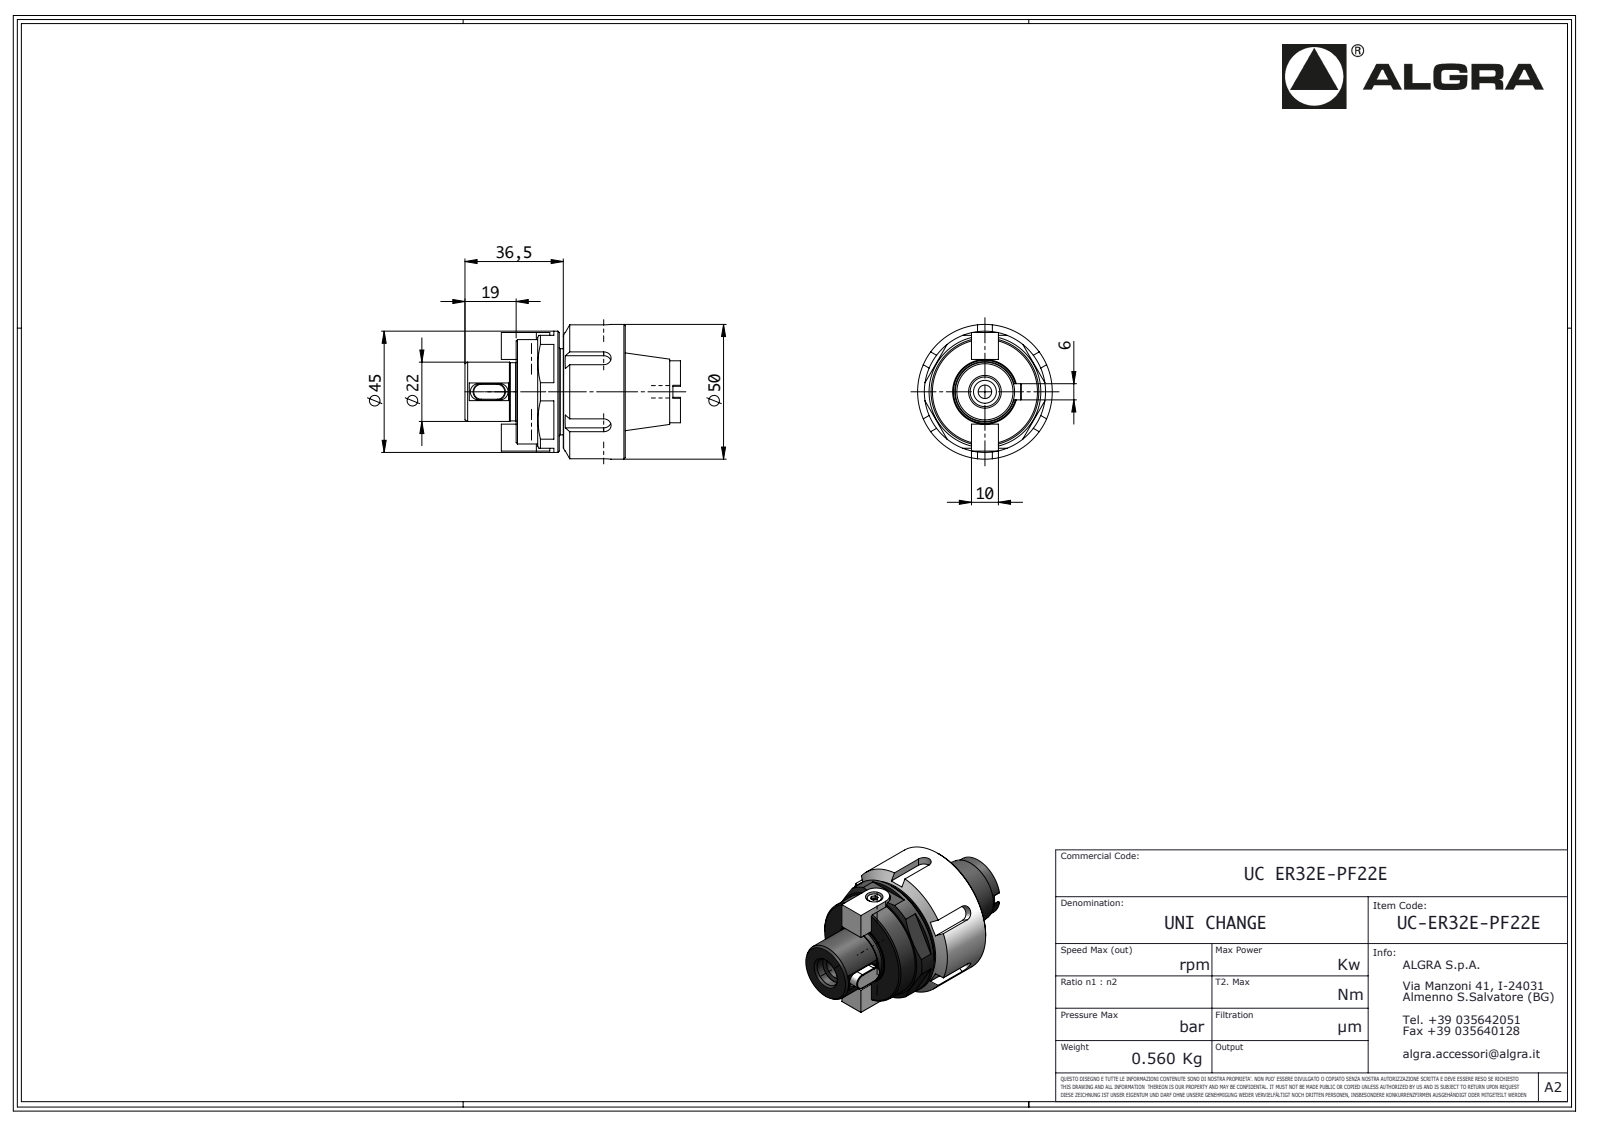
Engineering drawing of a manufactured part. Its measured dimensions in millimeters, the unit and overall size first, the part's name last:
Units: millimetres
Overall size (bounding box): 91.7 × 50 × 50
Round holes (diameter × count): ⌀2.1 ×1
Round bosses / shafts (diameter × count): ⌀50 ×1, ⌀45 ×1, ⌀40 ×1, ⌀31.6 ×1, ⌀23.65 ×1, ⌀22 ×1, ⌀21.6 ×1, ⌀6.37 ×1
Partial cylindrical surfaces — rounded edges, fillets, slot ends (radius × count): R0.33 ×7, R0.52 ×7, R3.7 ×7, R0.25 ×4, R3 ×4, R2.75 ×3, R5 ×2, R0.21 ×1
Main face-to-face distances: 23, 24.5, 16, 40.5, 1.5, 17.5, 1.05, 42.95, 5.5, 44
Volume: 90 978 mm³ · Surface area: 17 058 mm²
Bodies: 1 solid, 432 faces (284 planar, 56 cylindrical, 92 other)
Part name (STEP PRODUCT): UCER32E-PF22E
STEP written by: SolidWorks 2016 (AUTOMOTIVE_DESIGN)
